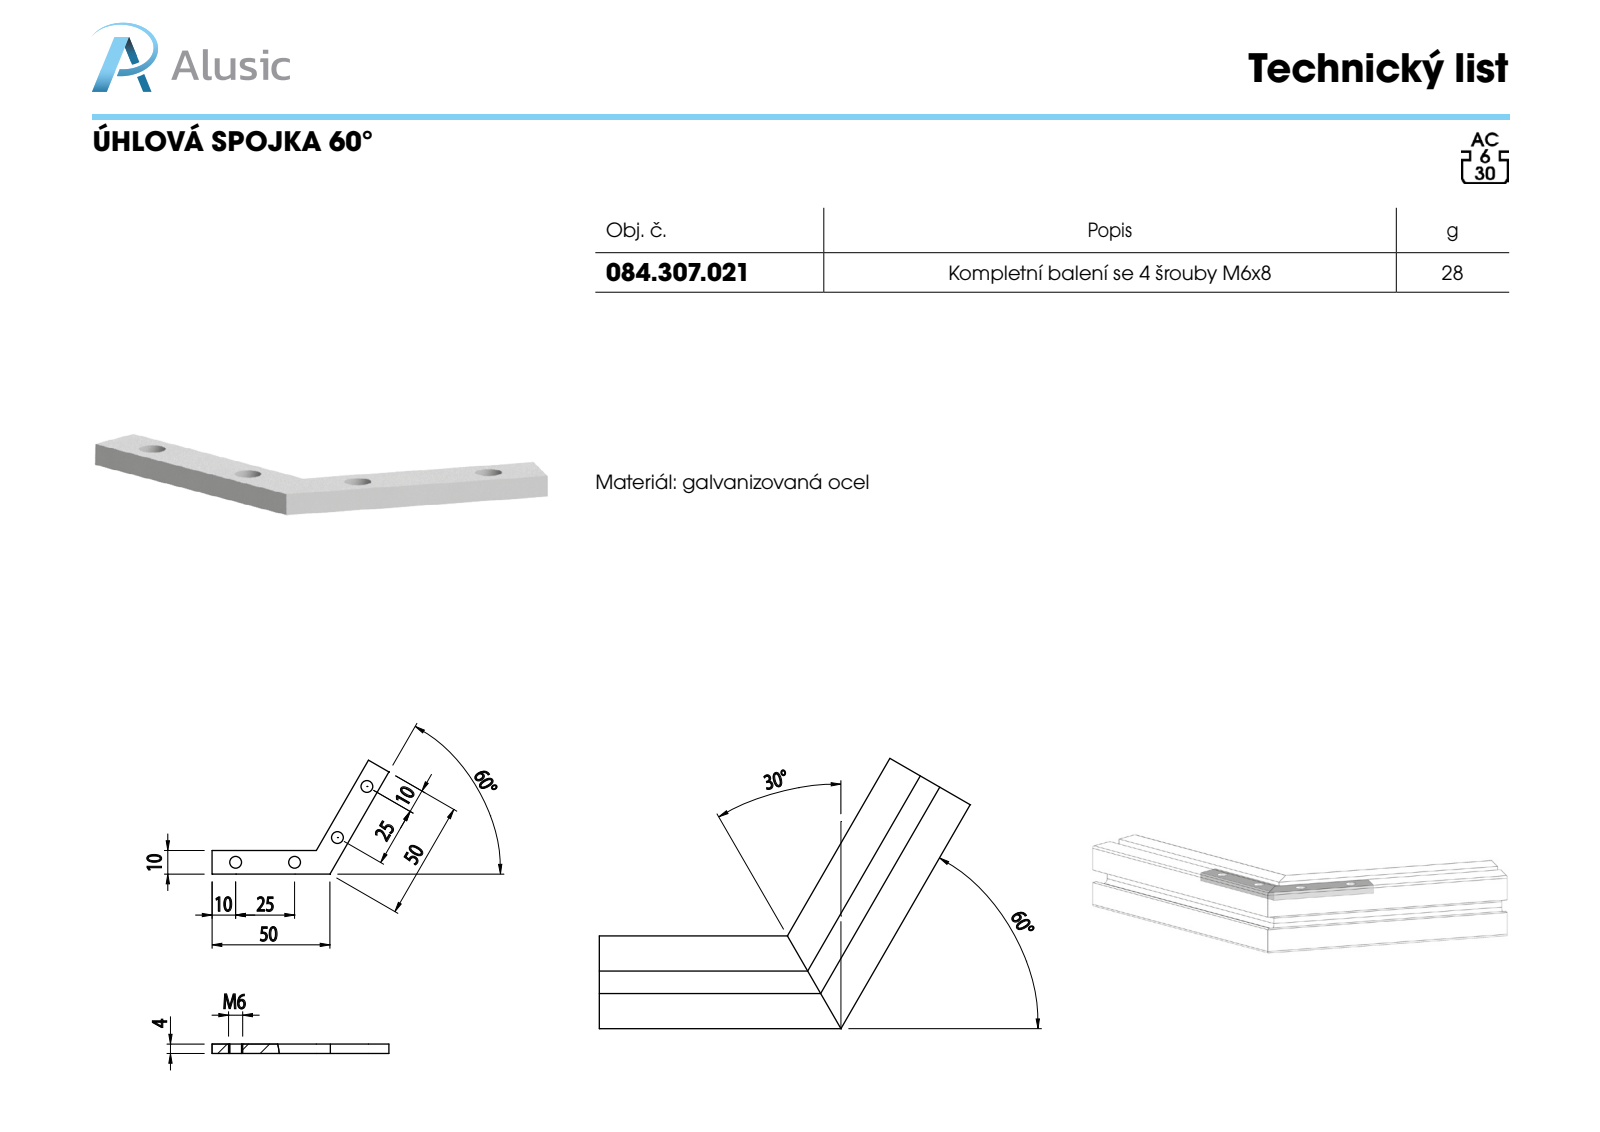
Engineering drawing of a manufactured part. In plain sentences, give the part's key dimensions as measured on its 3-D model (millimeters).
The part is named "084.307.021". Its 3-D file was written by "SolidWorks 2011 (CONFIG_CONTROL_DESIGN)". It is 1 solid with 16 faces: 8 planar, 8 cylindrical and 0 other. Overall it measures 75 by 48.3 by 4 millimeters. Its volume is 3 455 cubic millimeters and its surface area 2 813 square millimeters. Round holes: 4 of diameter 5. The main face-to-face distances are 4, 10. The hole center spacings are 25, 44.43, 20.98, 64.28.
